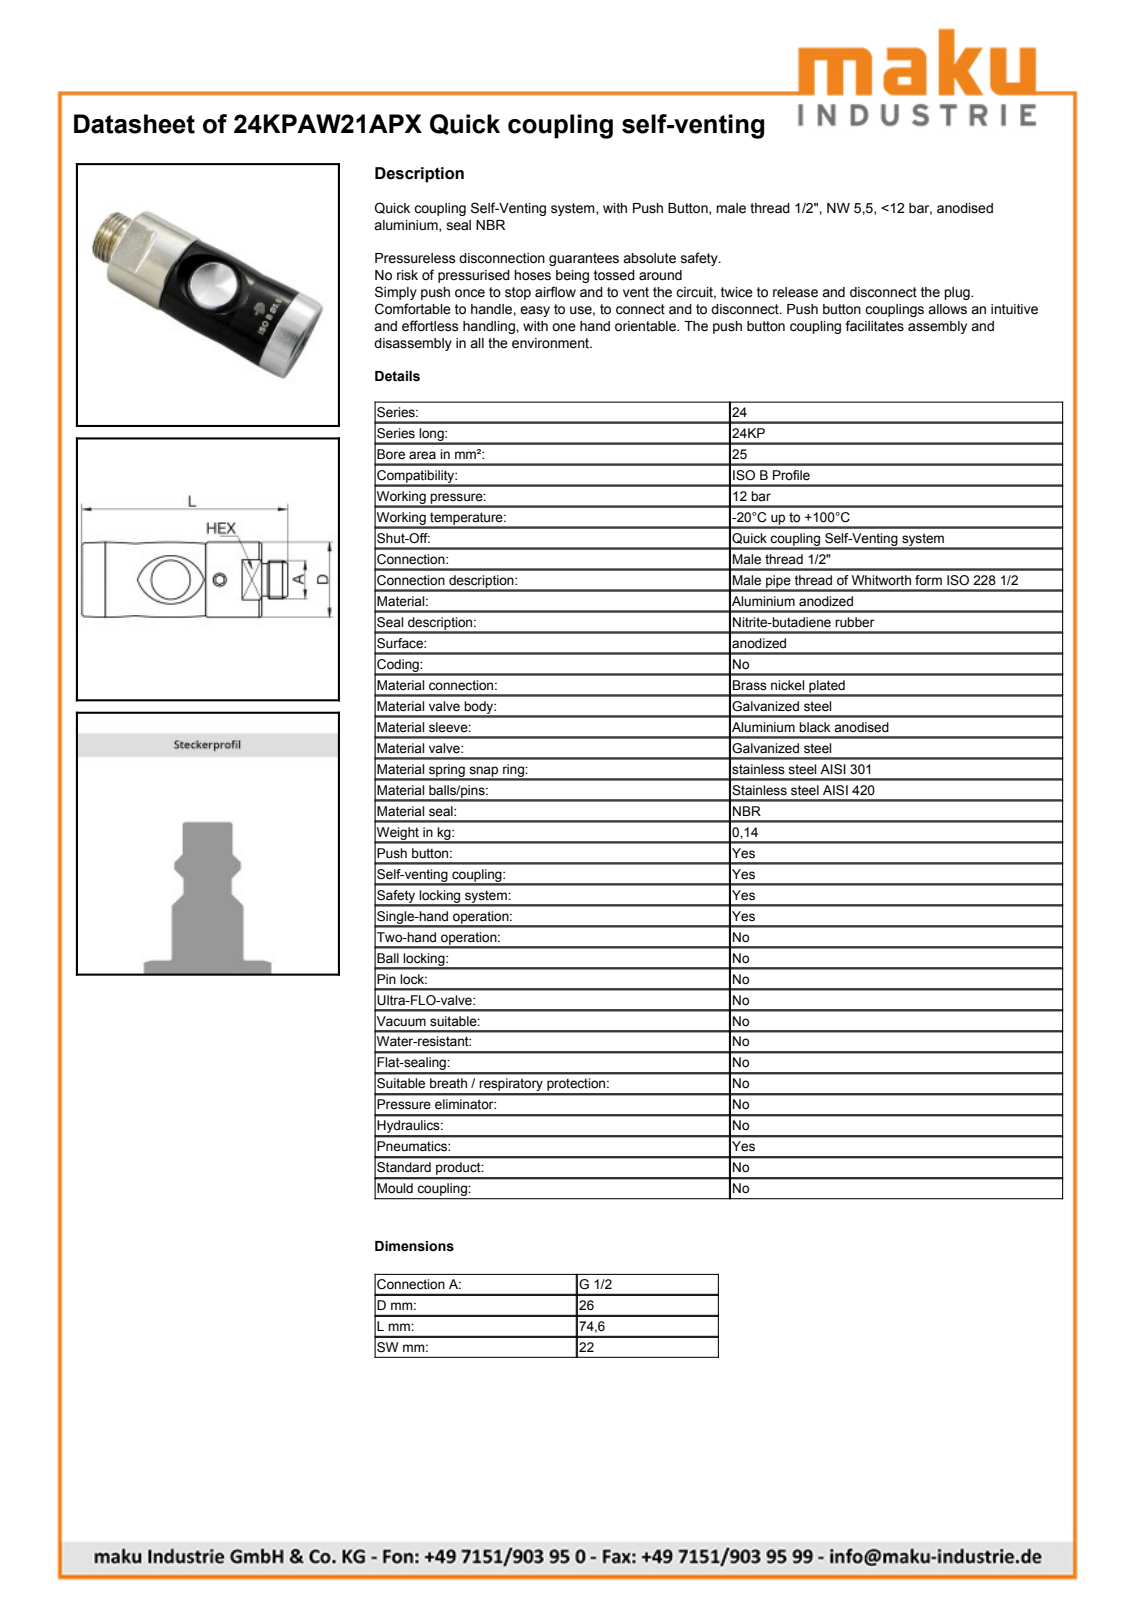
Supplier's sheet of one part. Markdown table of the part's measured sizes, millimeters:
| quantity | value |
| --- | --- |
| part name | 24KPAW21APX |
| STEP written by | Autodesk Inventor 2019 (CONFIG_CONTROL_DESIGN) |
| units | millimeters |
| bodies | 39 solids, 222 faces (62 planar, 70 cylindrical, 90 other) |
| overall size | 74.6 × 26 × 26 |
| volume | 39 814 mm³ |
| surface area | 24 784 mm² |
| round holes (diameter × count) | 12.4 × 2, 3.5 × 1, 6.5 × 1, 9.6 × 1, 9.65 × 1, 10.6 × 1, 12 × 1, 12.25 × 1, 13.6 × 1, 14 × 1, 15 × 1, 15.91 × 1 |
| round bosses / shafts (diameter × count) | 26 × 1, 22 × 1, 21.28 × 1, 20.5 × 1, 18.1 × 1, 16.5 × 1, 15.8 × 1, 15.8 × 1 |
| partial cylindrical surfaces (radius × count) | 6.2 × 2 |
| main face-to-face distances | 43.1, 35, 8.1, 1, 31.5, 66.5, 74.6, 12, 19.5, 54.5 |
| hole center spacings | 0.6, 0.7, 1.3, 17.05 |
